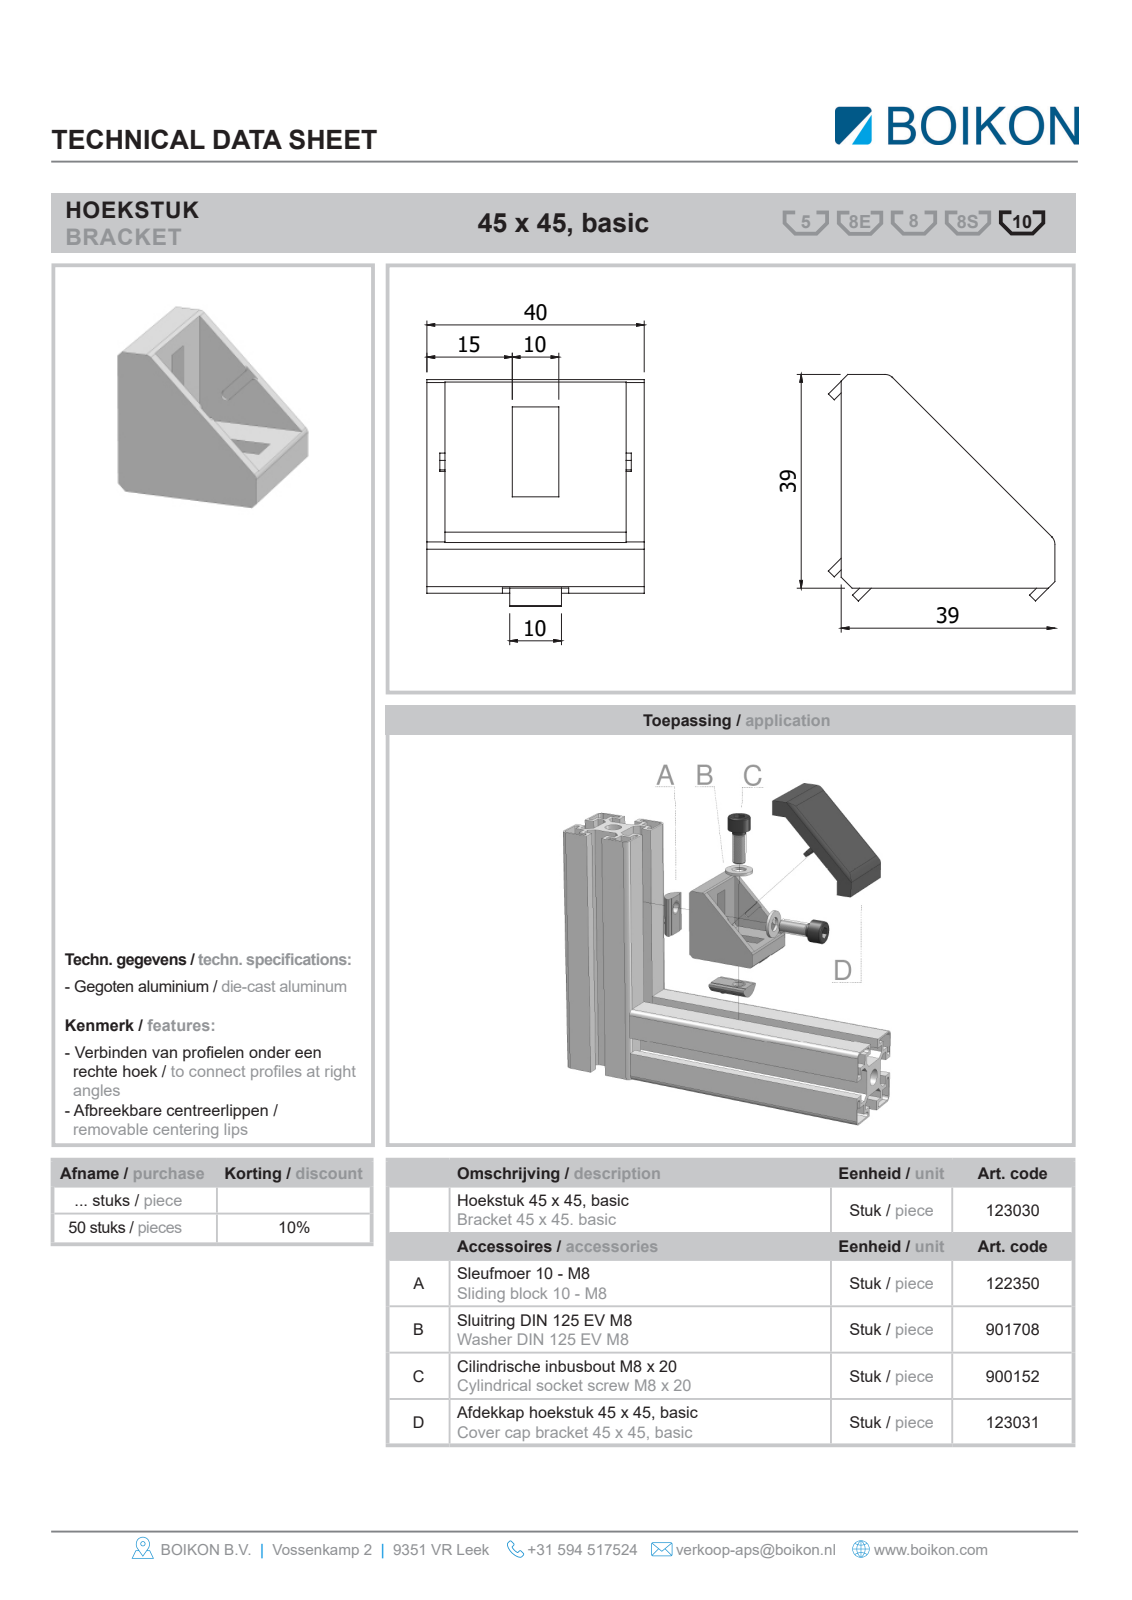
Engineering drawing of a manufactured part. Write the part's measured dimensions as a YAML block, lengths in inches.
part_name: "Root; 123030HOEKSTUK 45X45 BASICBOIKON; 900152Cil. inbusbout DIN 912 EV M8 x 20BOIKON0; 122350Sleufmoer 10 - M8 met kogelBOIKON (+2 more)"
step_written_by: "HiCAD 2013 1802.4 Build 509 (AUTOMOTIVE_DESIGN)"
units: inches
bodies: {solids: 8, faces: 222, planar: 183, cylindrical: 31, other: 8}
overall_size: [2.478, 2.478, 1.654]
volume: 2.142
surface_area: 40.14
round_holes:
  - {diameter: 0.315, count: 2}
  - {diameter: 0.331, count: 2}
round_bosses_or_shafts:
  - {diameter: 0.63, count: 2}
  - {diameter: 0.512, count: 2}
  - {diameter: 0.255, count: 2}
partial_cylinders:
  - {radius: 0.079, count: 5}
  - {radius: 0.039, count: 2}
  - {radius: 0.157, count: 2}
  - {radius: 0.276, count: 2}
  - {radius: 0.315, count: 2}
  - {radius: 0.059, count: 1}
face_to_face_distances: [0.118, 0.138, 0.236, 0.091, 1.516, 0.047, 1.654, 1.488, 0.512, 1.004]
